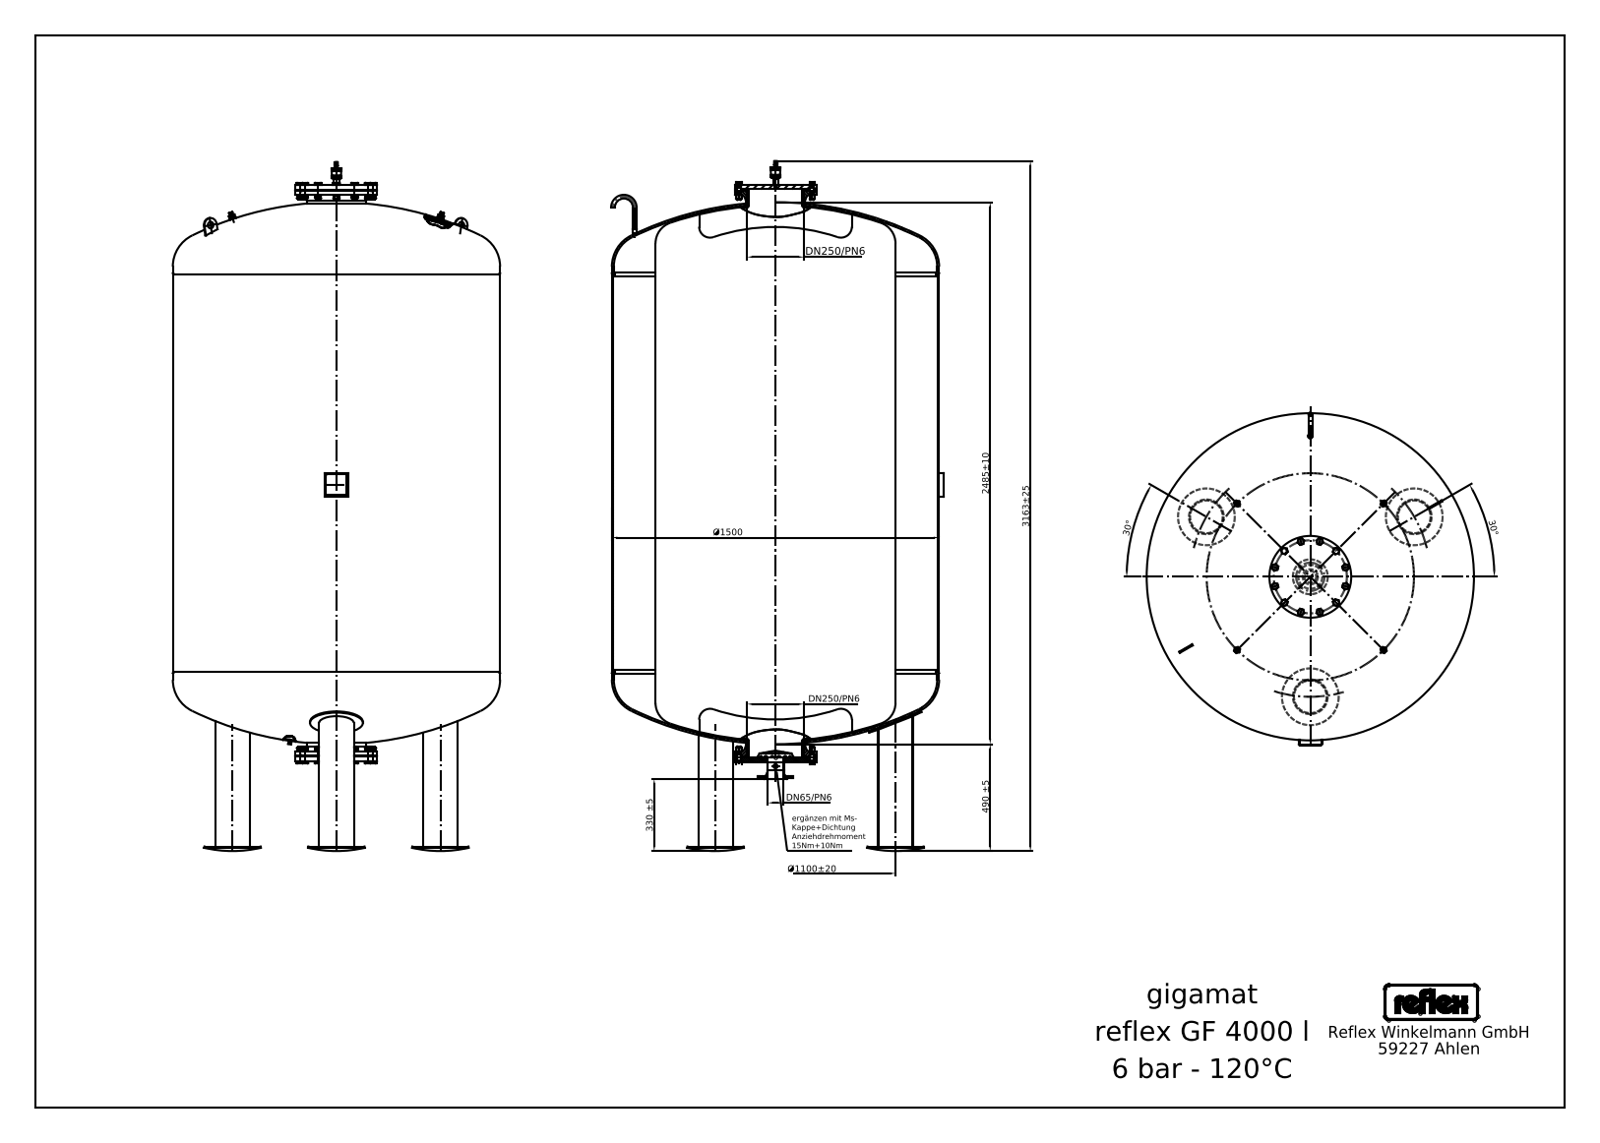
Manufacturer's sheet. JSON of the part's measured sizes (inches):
{"step_written_by": "Mechanical Desktop 2008 (CONFIG_CONTROL_DESIGN)", "units": "inches", "bodies": {"solids": 20, "faces": 812, "planar": 487, "cylindrical": 199, "other": 126}, "overall_size": [124.528, 59.055, 59.055], "volume_in3": 248900, "surface_area_in2": 35620, "round_holes": [[1.181, 1], [10.252, 1]], "round_bosses_or_shafts": [[0.63, 12], [6.26, 3], [0.654, 2], [0.472, 2], [59.055, 1], [14.764, 1], [10.748, 1], [10.724, 1]], "partial_cylinders_radius": [[0.332, 4], [0.133, 3], [0.227, 2], [0.398, 2], [0.548, 2], [0.555, 2], [0.75, 2], [0.166, 1]], "face_to_face_distances": [71.85, 0.866, 103.189, 1.063, 102.126, 87.165, 15.315, 88.031, 16.181, 16.024]}
